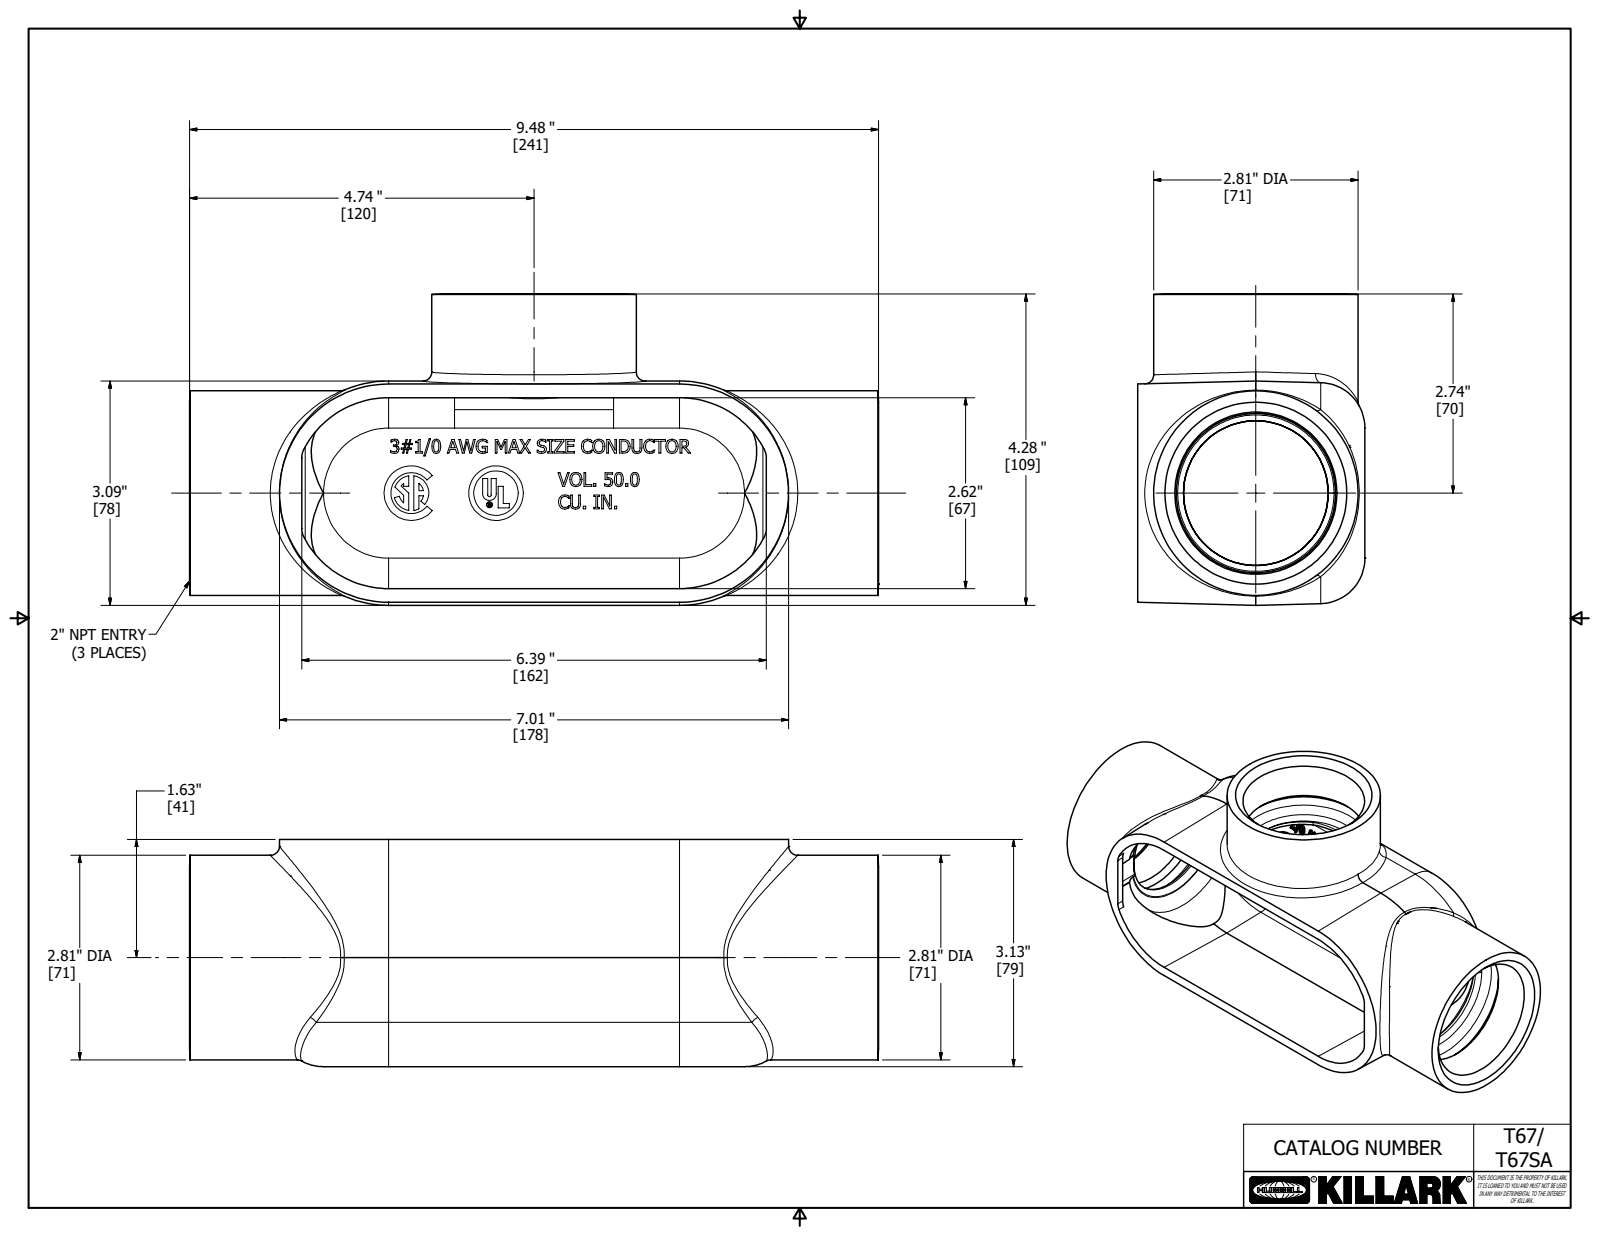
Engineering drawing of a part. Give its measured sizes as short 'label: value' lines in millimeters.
name: 17712-2
written by: Autodesk Inventor 2018 (AUTOMOTIVE_DESIGN)
unit: mm
bodies: 1 solid, 854 faces (502 planar, 39 cylindrical, 313 other)
size: 240.7 × 108.7 × 79.4
volume: 306 800 mm³; area: 120 200 mm²
holes: 2× ⌀60.5, 1× ⌀1.8, 1× ⌀15.5, 1× ⌀66.7
bosses: 2× ⌀71.4, 1× ⌀19.1, 1× ⌀2.1
rounds: 4× R1.3, 4× R3.2, 2× R11.1, 2× R15.9, 1× R0.2, 1× R0.3, 1× R0.6, 1× R2.4
face distances: 4.7, 73.6, 68.8, 78.4, 79.4, 74.6, 4, 5.6, 0.8, 78.6
hole spacings: 4.6
